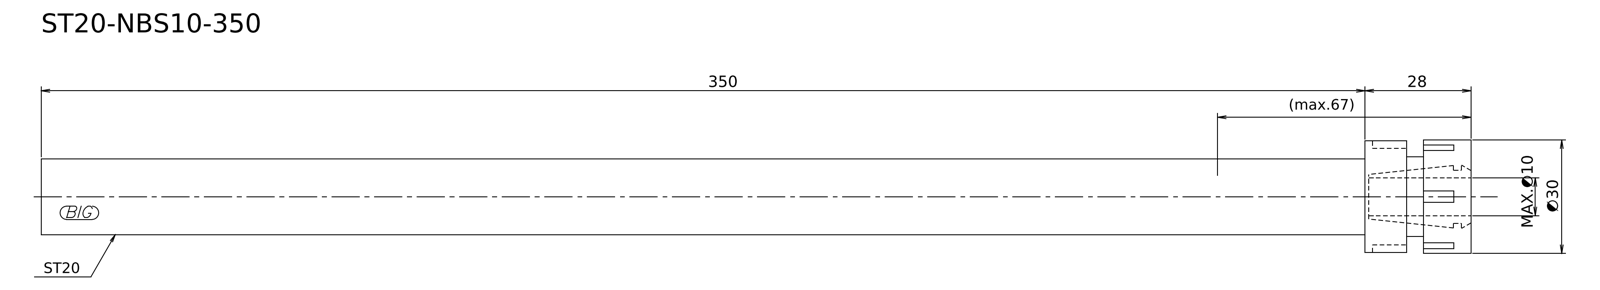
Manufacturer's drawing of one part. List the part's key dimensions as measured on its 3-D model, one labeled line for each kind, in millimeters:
STEP written by: Kubotek KeyCreator V8.5.1 (14335) (CONFIG_CONTROL_DESIGN)
Units: millimetres
Bodies: 1 solid, 9 faces (5 planar, 4 cylindrical, 0 other)
Overall size (bounding box): 378 × 30 × 30
Volume: 127 869 mm³ · Surface area: 26 574 mm²
Round bosses / shafts (diameter × count): ⌀30 ×1, ⌀29.5 ×1, ⌀21 ×1, ⌀20 ×1
Main face-to-face distances: 28, 12.5, 15.5, 17, 4.5, 11, 378, 365.5, 361, 350
